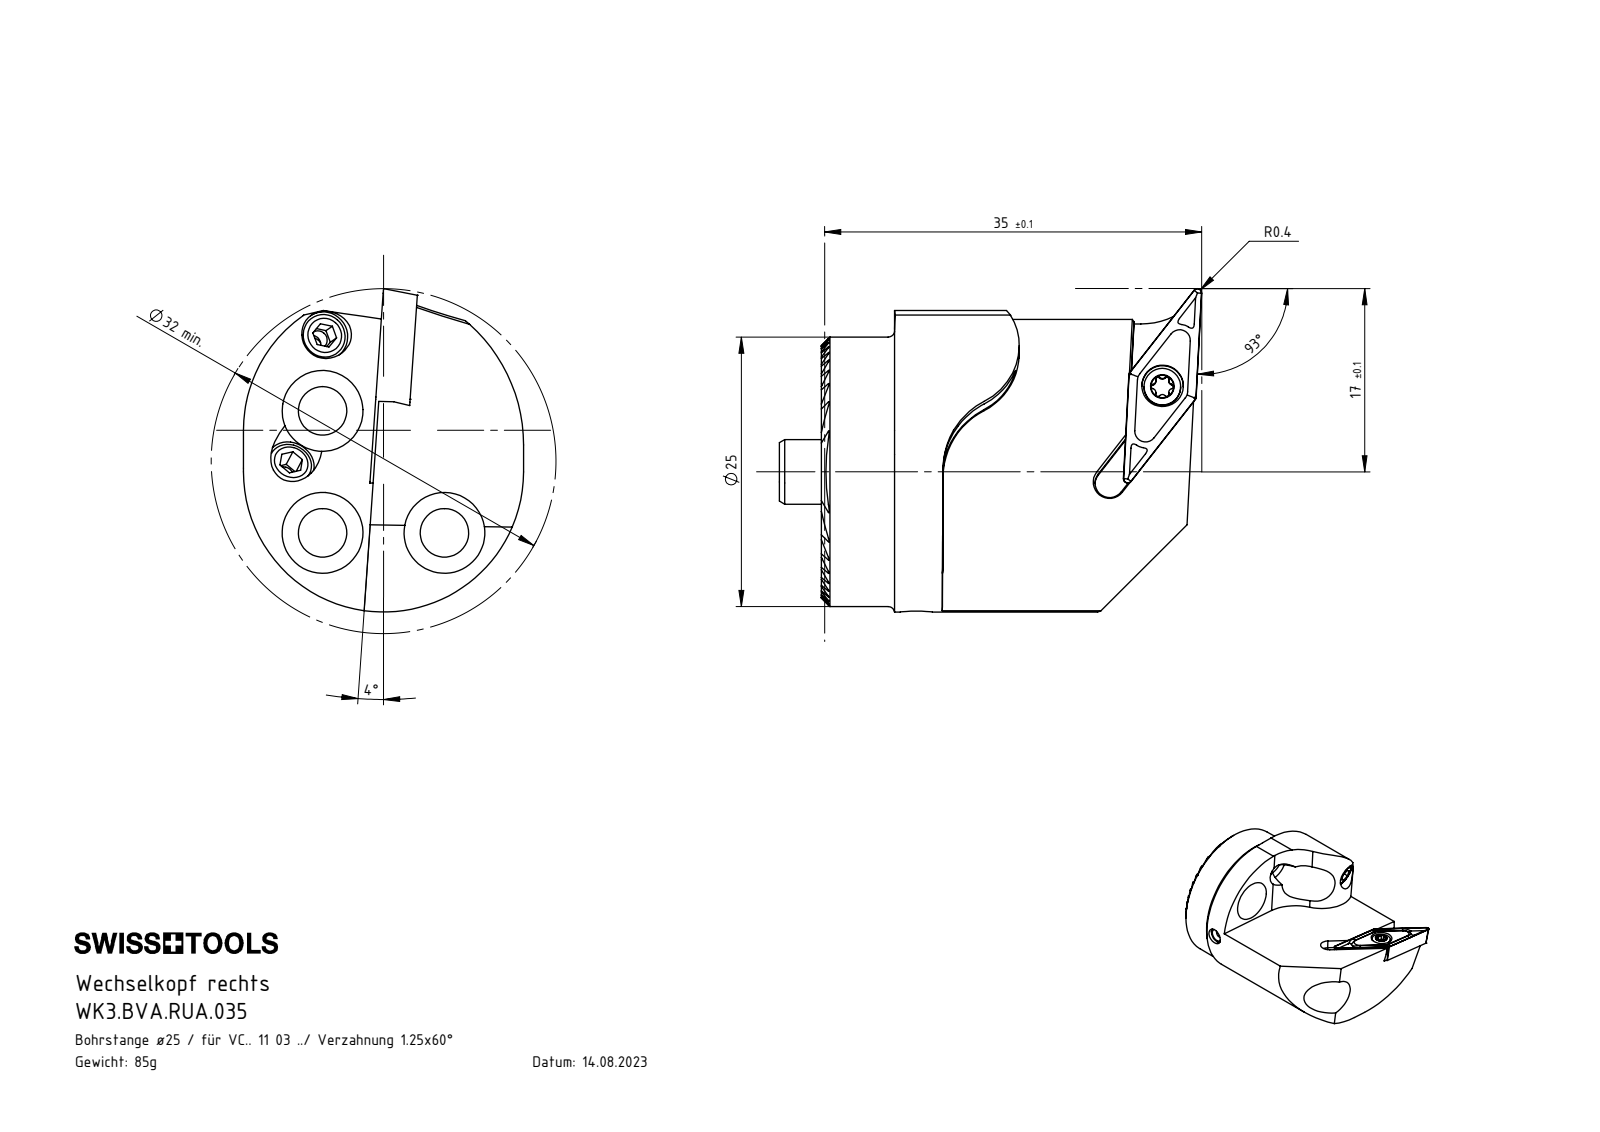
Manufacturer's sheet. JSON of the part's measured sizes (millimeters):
{"part_name": "WKX-ER1.004.005_A_PreviewCfg; WK3-BVA.RUA.035_A_Fertigbearbeitung; WK3-ER1.001.006_A_Fertigbearbeitung; WK3.BVA.RUA.035 (+3 more)", "step_written_by": "SolidWorks 2017 (AUTOMOTIVE_DESIGN)", "units": "millimeters", "bodies": {"solids": 12, "faces": 377, "planar": 179, "cylindrical": 94, "other": 104}, "overall_size": [39.2, 30, 26], "volume_mm3": 10742, "surface_area_mm2": 6782, "round_holes": [[2.38, 3], [2.5, 3], [4.2, 3], [4.5, 3], [7.5, 3], [1.7, 2], [3, 2], [3.3, 2], [2.05, 1], [2.8, 1], [3.85, 1], [6, 1]], "round_bosses_or_shafts": [[3, 3], [4, 2], [25, 1], [3.4, 1], [2.5, 1]], "partial_cylinders_radius": [[0.12, 20], [0.21, 6], [0.36, 4], [0.36, 2], [7, 2], [13, 2], [1.35, 1], [6, 1]], "face_to_face_distances": [4.33, 1.08, 3.25, 5.41, 8.66, 7.58, 2.16, 2.17, 9.74, 6.5], "hole_center_spacings": [8, 11.32, 16.01]}
